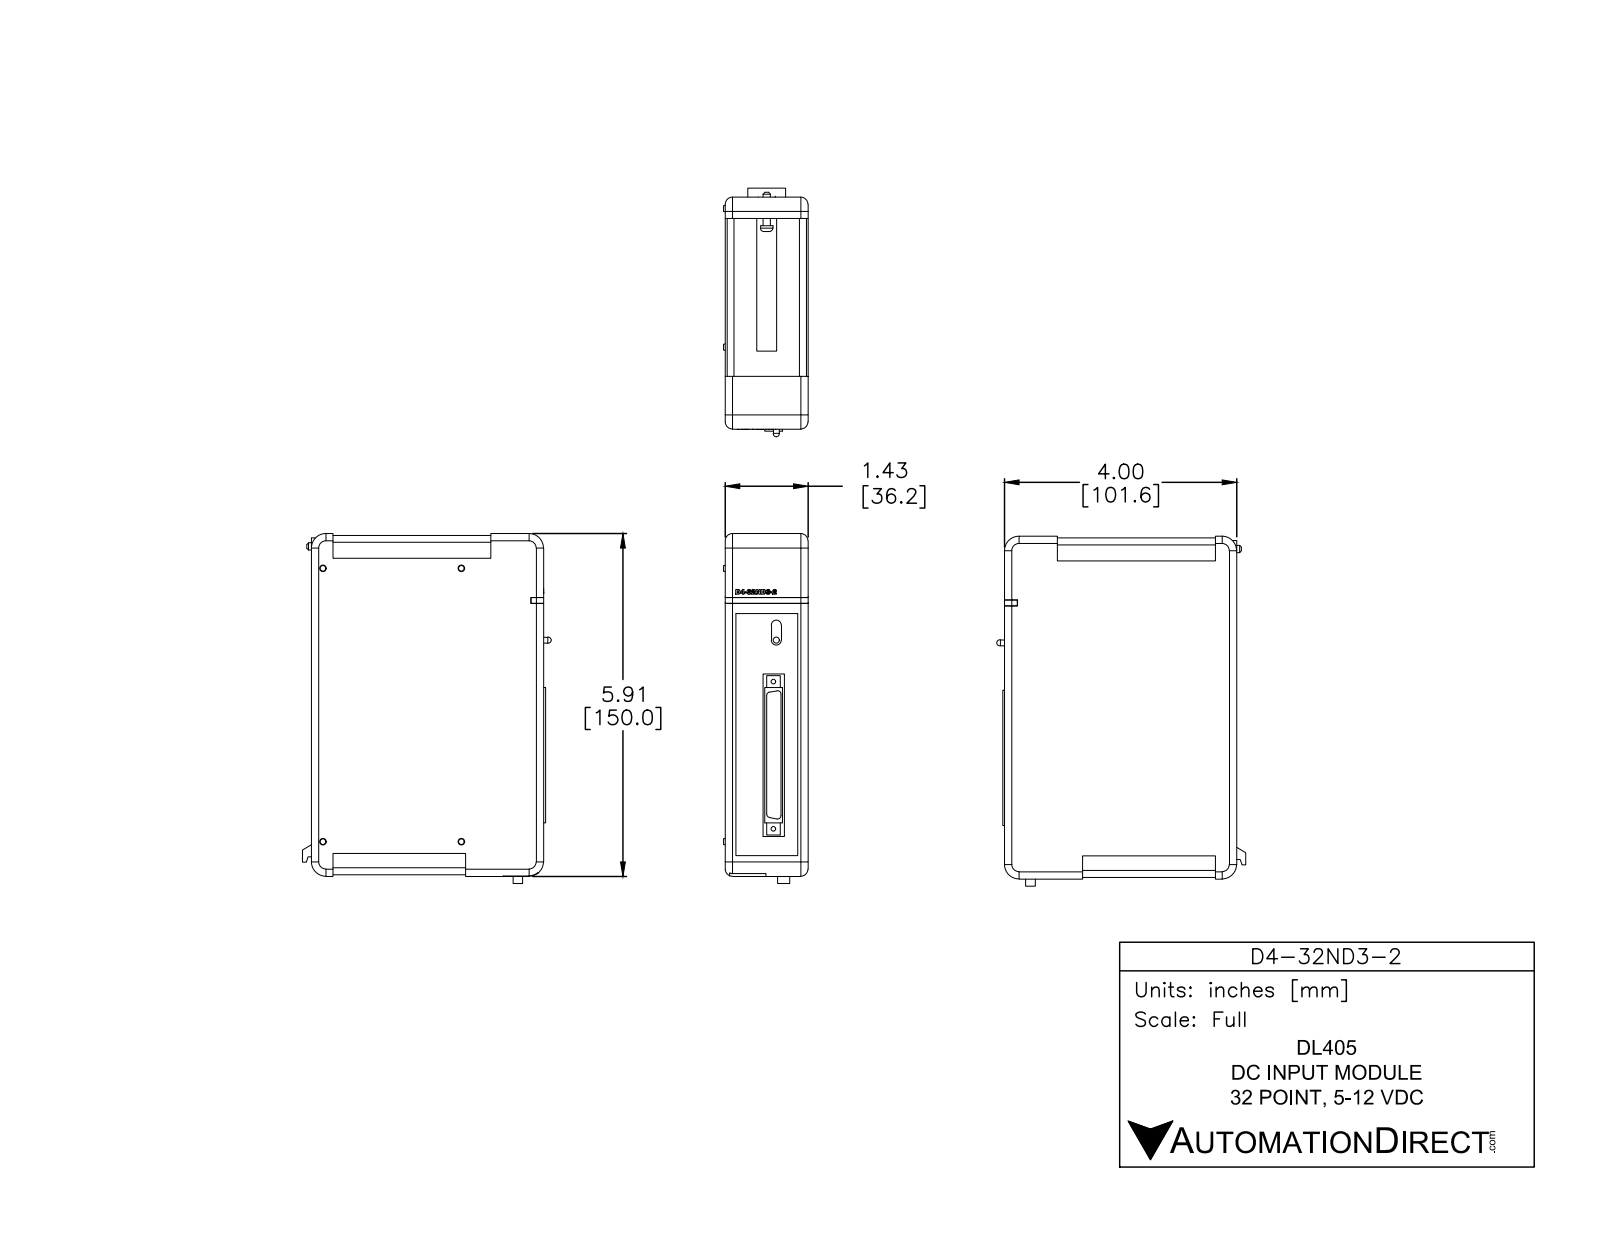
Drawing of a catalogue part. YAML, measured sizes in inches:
part_name: "D4-32ND3-2"
step_written_by: "SolidWorks 2014 (AUTOMOTIVE_DESIGN)"
units: inches
bodies: {solids: 2, faces: 331, planar: 199, cylindrical: 46, other: 86}
overall_size: [6.025, 4.285, 1.455]
volume: 32.07
surface_area: 83.59
round_holes:
  - {diameter: 0.08, count: 2}
round_bosses_or_shafts:
  - {diameter: 0.212, count: 1}
  - {diameter: 0.123, count: 1}
  - {diameter: 0.1, count: 1}
partial_cylinders:
  - {radius: 0.125, count: 8}
  - {radius: 0.06, count: 4}
  - {radius: 0.12, count: 4}
  - {radius: 0.25, count: 4}
  - {radius: 0.085, count: 2}
  - {radius: 0.145, count: 1}
  - {radius: 0.171, count: 1}
face_to_face_distances: [1.425, 0.03, 3.97, 1.395, 5.845, 5.875, 4, 0.2, 3.77, 3.8]
hole_center_spacings: [2.538]
